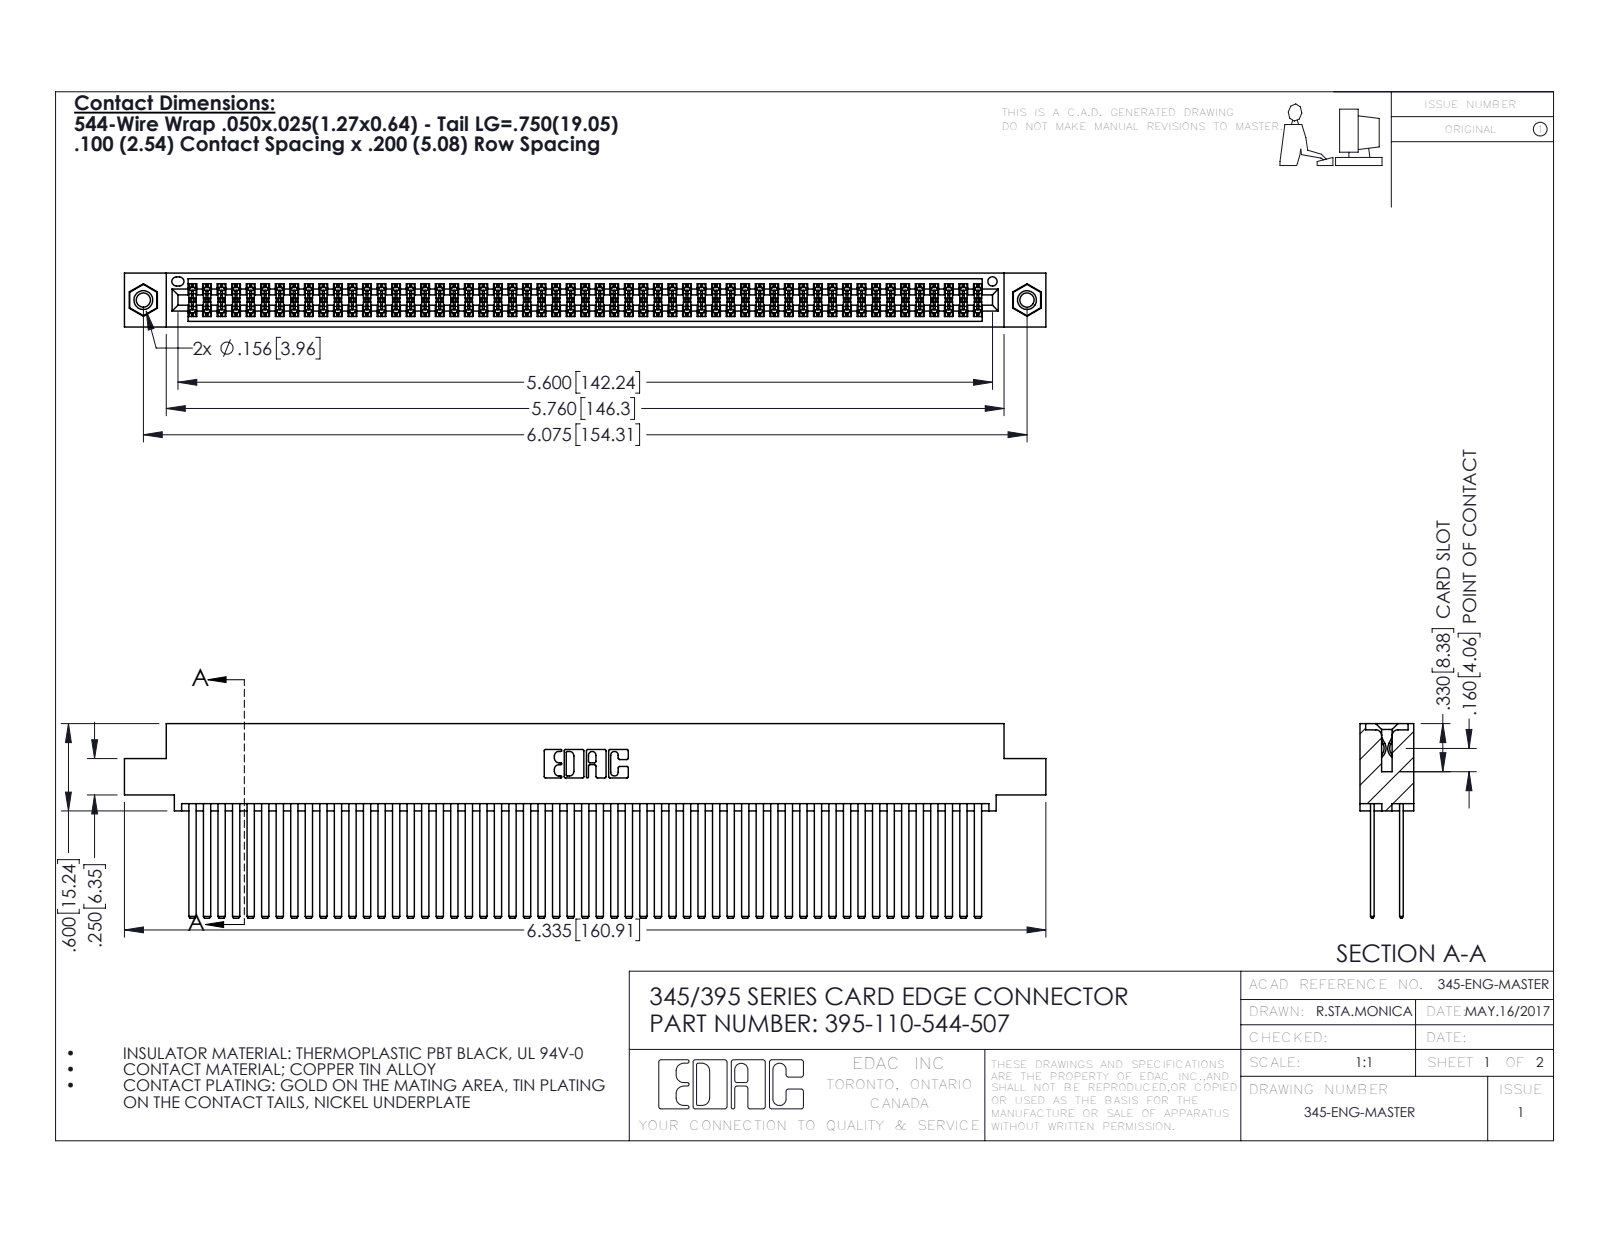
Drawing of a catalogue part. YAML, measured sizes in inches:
part_name: "345-292-001_345-293-144; 345-250-001_345-250-005-103; 345 Part_0.110 Offset - 0.156 Dia-TI; 395-110-544-507"
step_written_by: "SolidWorks 2016 (CONFIG_CONTROL_DESIGN)"
units: inches
bodies: {solids: 113, faces: 5030, planar: 3306, cylindrical: 1708, other: 16}
overall_size: [6.335, 1.337, 0.37]
volume: 1.05
surface_area: 47.01
round_holes:
  - {diameter: 0.098, count: 2}
  - {diameter: 0.125, count: 2}
  - {diameter: 0.156, count: 2}
  - {diameter: 0.064, count: 1}
round_bosses_or_shafts:
  - {diameter: 0.155, count: 2}
partial_cylinders:
  - {radius: 0.006, count: 165}
  - {radius: 0.01, count: 22}
  - {radius: 0.007, count: 6}
  - {radius: 0.031, count: 6}
  - {radius: 0.026, count: 3}
  - {radius: 0.014, count: 2}
  - {radius: 0.019, count: 2}
  - {radius: 0.022, count: 2}
face_to_face_distances: [0.2, 0.025, 0.072, 0.098, 0.272, 0.298, 0.225, 0.175, 0.37, 0.05]
hole_center_spacings: [0.27, 5.839, 6.075]
